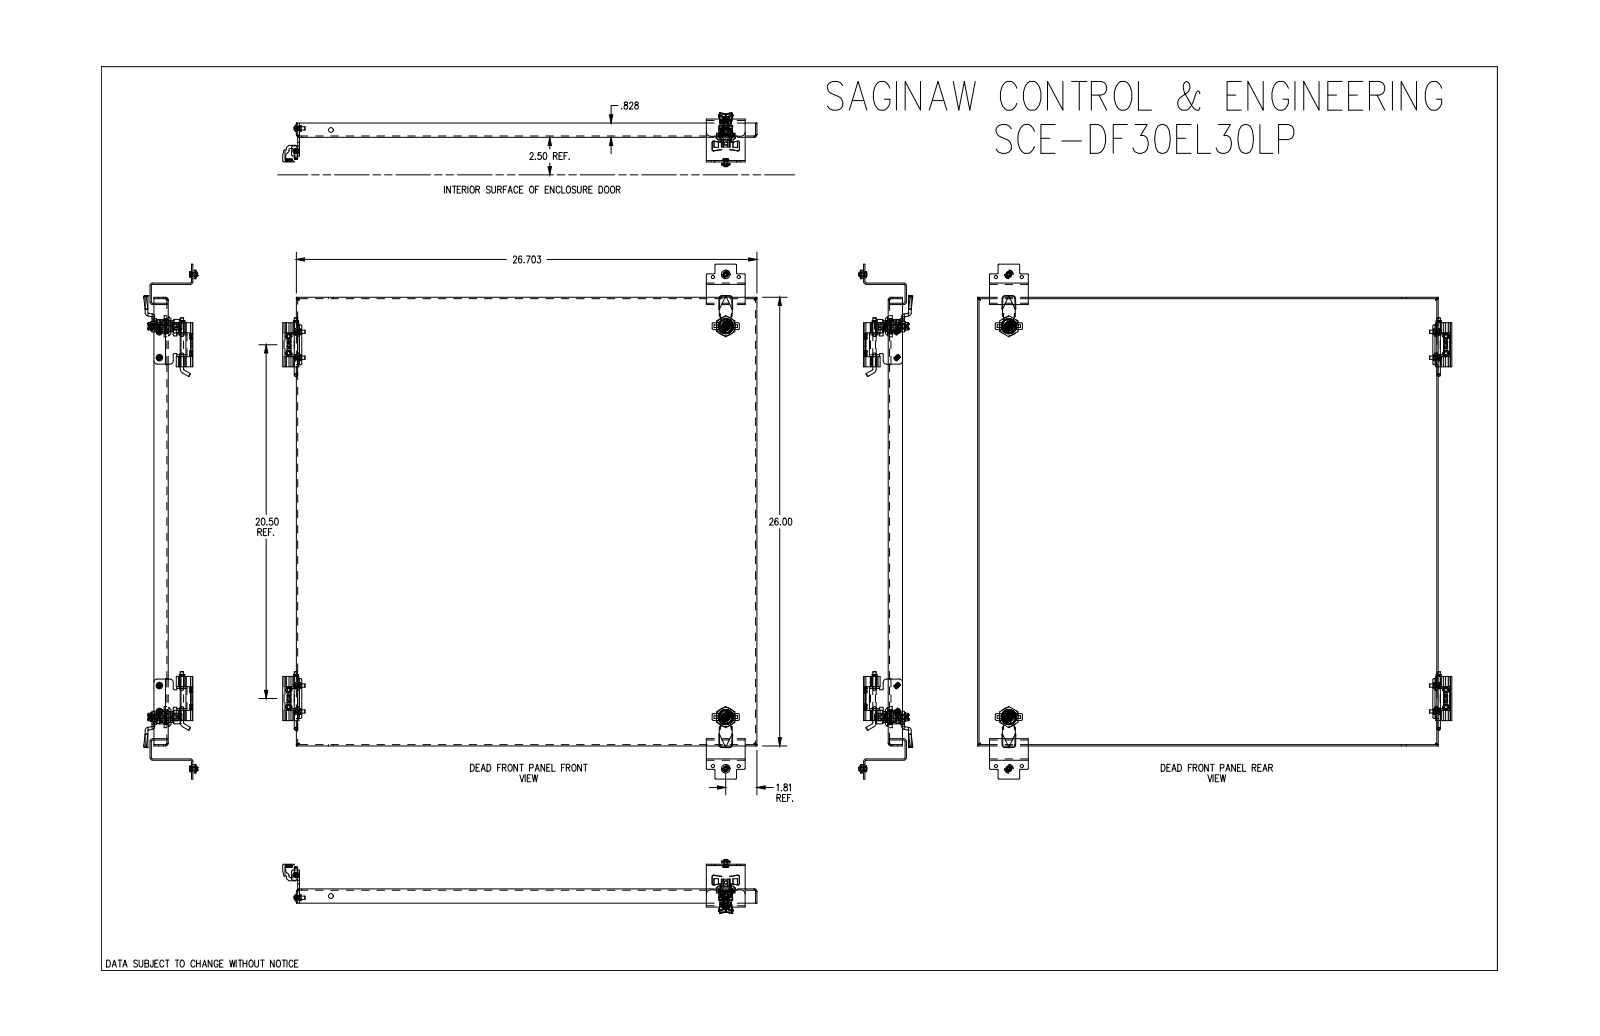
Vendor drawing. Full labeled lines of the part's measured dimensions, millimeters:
Part name (STEP PRODUCT): SCE-DF30EL30LP
STEP written by: SolidWorks 2022 (AUTOMOTIVE_DESIGN)
Units: millimetres
Bodies: 35 solids, 1243 faces (547 planar, 390 cylindrical, 306 other)
Overall size (bounding box): 757.9 × 698.3 × 79.2
Volume: 865 600 mm³ · Surface area: 1 090 000 mm²
Round holes (diameter × count): ⌀4.8 ×6, ⌀6.4 ×6, ⌀4.3 ×4, ⌀4.8 ×4, ⌀5.3 ×4, ⌀5 ×2, ⌀6.3 ×2, ⌀10 ×2, ⌀11 ×2, ⌀16.1 ×2, ⌀5.6 ×1
Round bosses / shafts (diameter × count): ⌀8.6 ×6, ⌀9.5 ×4, ⌀6.3 ×4, ⌀4.8 ×4, ⌀5 ×3, ⌀28 ×2, ⌀19.8 ×2, ⌀16 ×2
Partial cylindrical surfaces — rounded edges, fillets, slot ends (radius × count): R4 ×16, R1.3 ×13, R1.5 ×9, R1.5 ×8, R2 ×8, R1.7 ×6, R1.6 ×5, R2.6 ×5
Main face-to-face distances: 1.5, 658.9, 1.5, 676.7, 2, 660.4, 657.4, 678.3, 675.2, 21
Hole centre spacings: 19.5, 38.1, 520.7, 647.8, 724, 74.7, 25, 76.2
